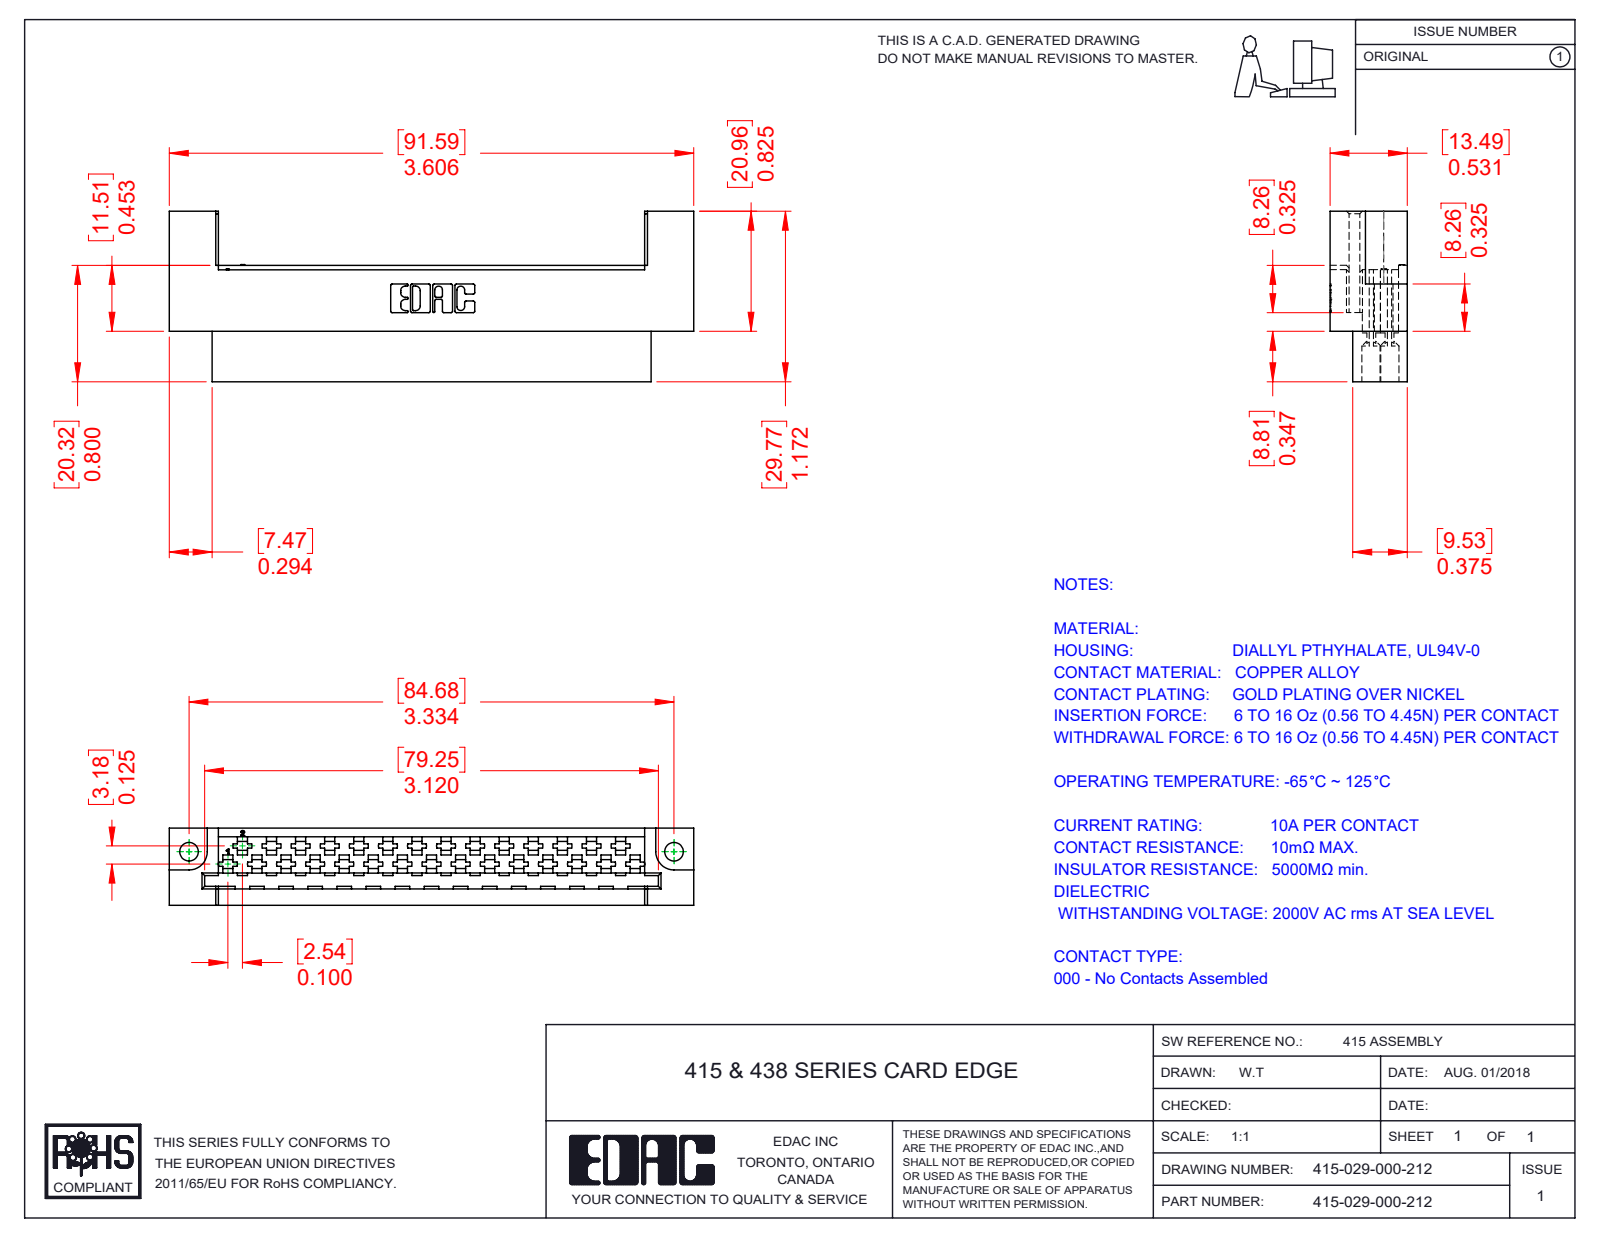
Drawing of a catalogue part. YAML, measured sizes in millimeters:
part_name: "415-029-000-212; 415-210-001_415-210-029-212"
step_written_by: "SolidWorks 2016 (CONFIG_CONTROL_DESIGN)"
units: millimeters
bodies: {solids: 1, faces: 914, planar: 701, cylindrical: 104, other: 109}
overall_size: [91.59, 29.77, 13.49]
volume: 15336
surface_area: 14737
round_holes:
  - {diameter: 3.3, count: 29}
  - {diameter: 3.25, count: 2}
partial_cylinders:
  - {radius: 0.25, count: 22}
  - {radius: 0.17, count: 6}
  - {radius: 0.8, count: 6}
  - {radius: 0.67, count: 3}
  - {radius: 3.17, count: 2}
face_to_face_distances: [13.49, 9.53, 3.96, 1.23, 3.17, 1.2, 0.74, 1.94, 3.15, 1.97]
hole_center_spacings: [4.06, 5.08, 8.25, 10.16, 13.09, 15.24, 18.06, 20.32]
